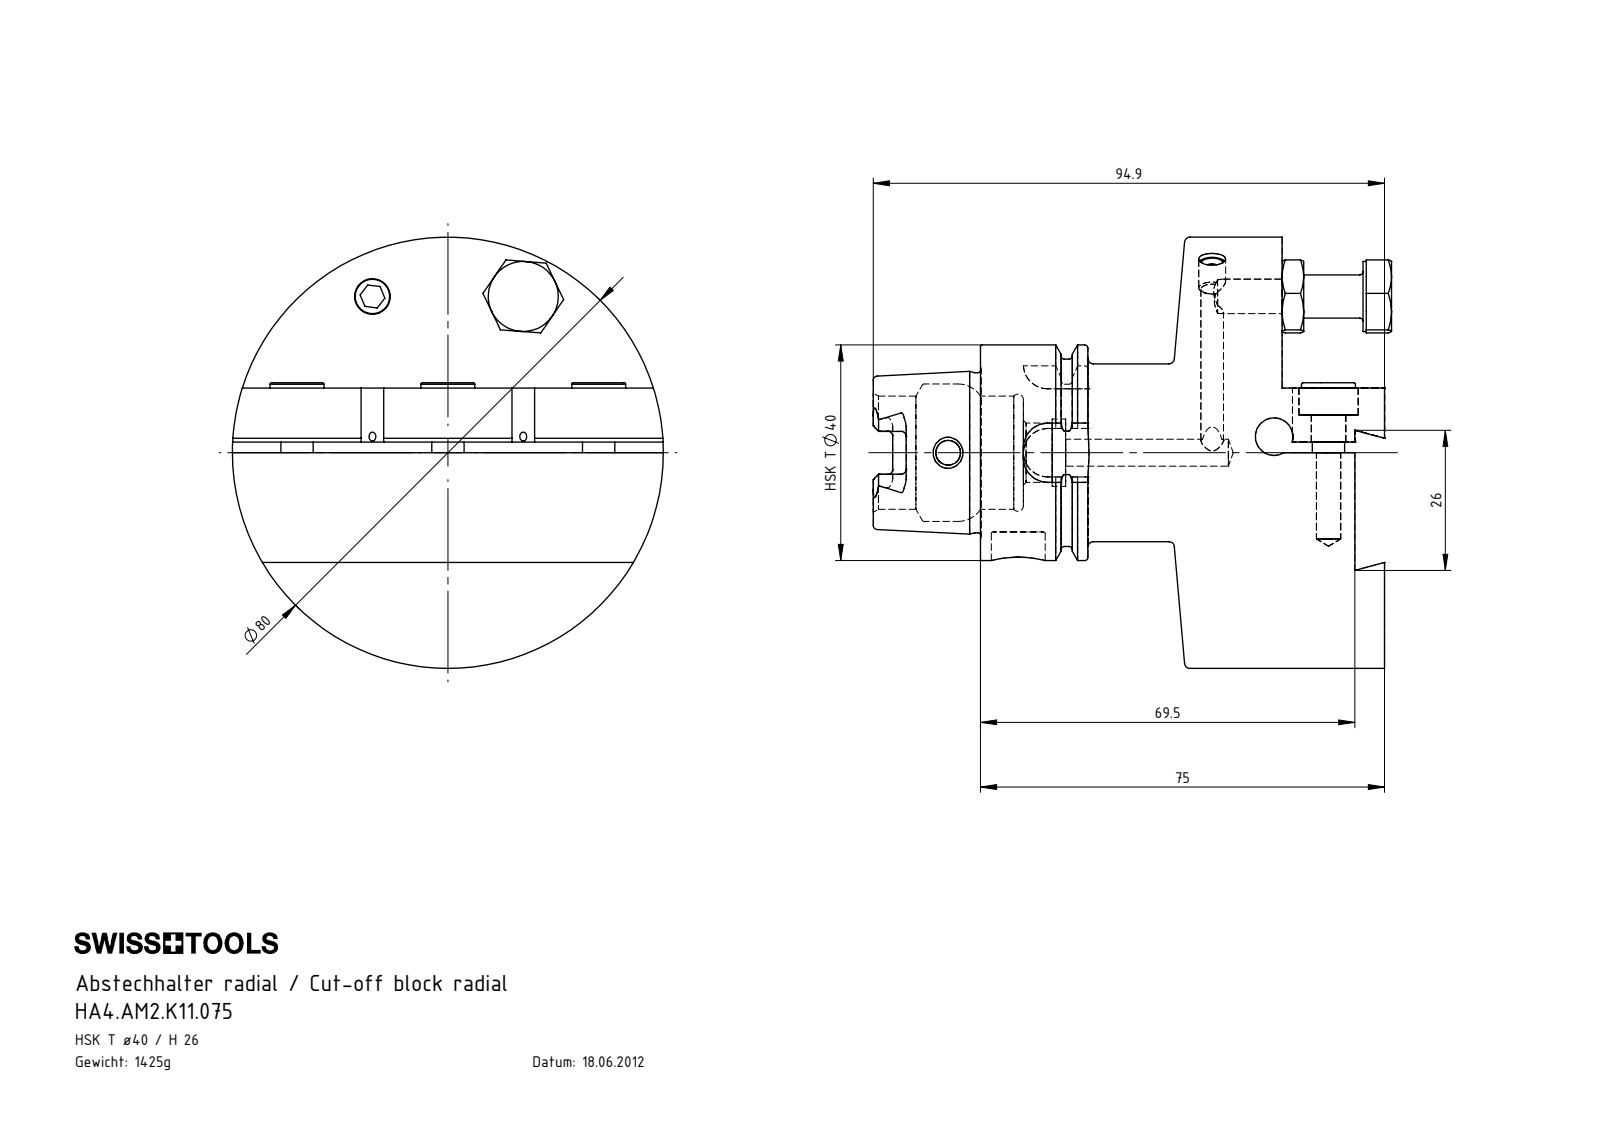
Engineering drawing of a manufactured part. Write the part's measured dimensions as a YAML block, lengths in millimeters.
part_name: "ISO 4762 - M6 x 16_PreviewCfg; KVT_MB_600_050; ISO 4026 - M8 x 10_PreviewCfg; AM3-ER1.001.020_PreviewCfg (+3 more)"
step_written_by: "SolidWorks 2017 (AUTOMOTIVE_DESIGN)"
units: millimeters
bodies: {solids: 11, faces: 468, planar: 151, cylindrical: 125, other: 192}
overall_size: [96.2, 80, 80]
volume: 174808
surface_area: 39271
round_holes:
  - {diameter: 6.4, count: 5}
  - {diameter: 11, count: 4}
  - {diameter: 4, count: 3}
  - {diameter: 4.5, count: 3}
  - {diameter: 4.2, count: 2}
  - {diameter: 7, count: 2}
  - {diameter: 3, count: 1}
  - {diameter: 4.6, count: 1}
  - {diameter: 5, count: 1}
  - {diameter: 10, count: 1}
  - {diameter: 12.5, count: 1}
  - {diameter: 21, count: 1}
round_bosses_or_shafts:
  - {diameter: 10, count: 3}
  - {diameter: 6, count: 3}
  - {diameter: 8, count: 2}
  - {diameter: 5, count: 2}
  - {diameter: 80, count: 1}
  - {diameter: 40, count: 1}
  - {diameter: 34.75, count: 1}
  - {diameter: 33, count: 1}
partial_cylinders:
  - {radius: 0.9, count: 6}
  - {radius: 1.88, count: 4}
  - {radius: 4.5, count: 4}
  - {radius: 2.1, count: 2}
face_to_face_distances: [14.5, 4.5, 19, 12, 2.4, 9.6, 4, 56, 70.5, 75]
hole_center_spacings: [28, 32.2, 63.96, 56, 57.5, 60.57]
